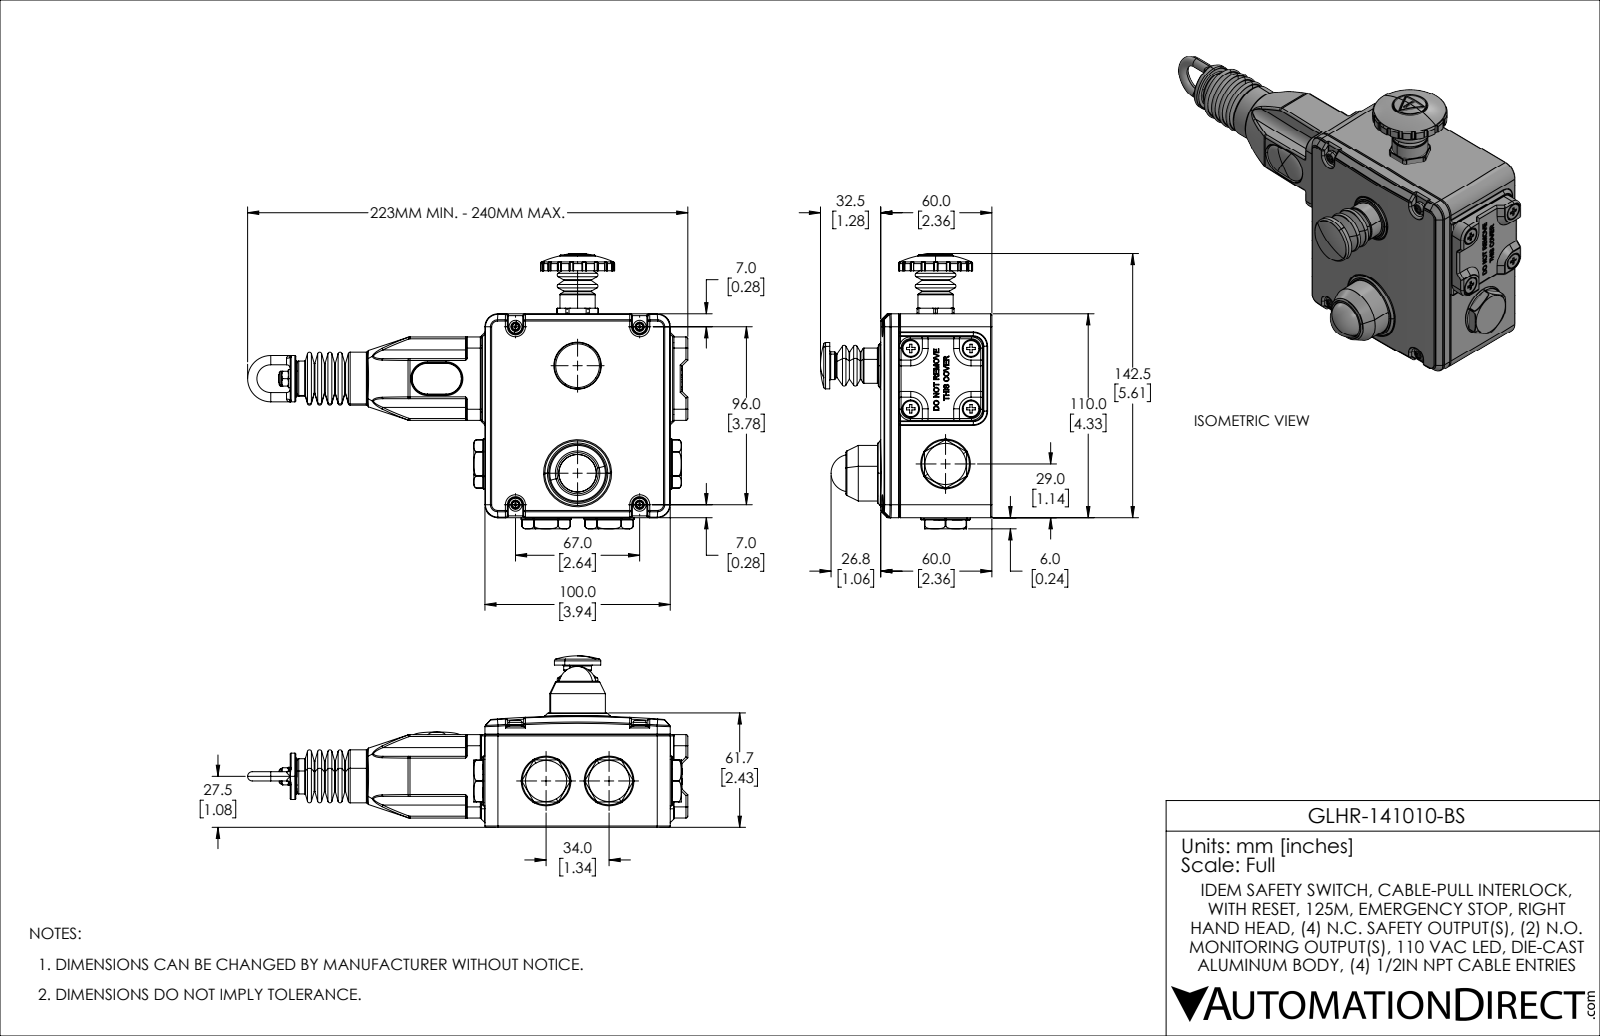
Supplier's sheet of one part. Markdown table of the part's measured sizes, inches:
| quantity | value |
| --- | --- |
| part name | GLHR-141010-BS |
| STEP written by | SolidWorks 2021 (AUTOMOTIVE_DESIGN) |
| units | inches |
| bodies | 43 solids, 4892 faces (1501 planar, 1613 cylindrical, 1778 other) |
| overall size | 9.354 × 5.847 × 3.642 |
| volume | 18.8 in³ |
| surface area | 299.9 in² |
| round holes (diameter × count) | 0.197 × 11, 0.209 × 9, 0.374 × 7, 0.354 × 6, 0.13 × 4, 0.157 × 4, 0.189 × 4, 0.213 × 4, 0.228 × 4, 0.067 × 3, 0.102 × 3, 0.118 × 3 |
| round bosses / shafts (diameter × count) | 0.335 × 7, 0.236 × 7, 0.173 × 7, 0.197 × 6, 0.276 × 5, 0.138 × 4, 0.051 × 4, 1.055 × 3 |
| partial cylindrical surfaces (radius × count) | 0.02 × 241, 0.039 × 158, 0.008 × 148, 0.028 × 72, 0.012 × 26, 0.006 × 14, 0.004 × 13, 0.236 × 12 |
| main face-to-face distances | 0.138, 2.157, 0.114, 2.043, 4.331, 0.055, 0.079, 0.157, 4.016, 3.878 |
| hole center spacings | 1.28, 1.281, 0.228, 0.374, 0.905, 1.891, 1.913, 3.012 |
